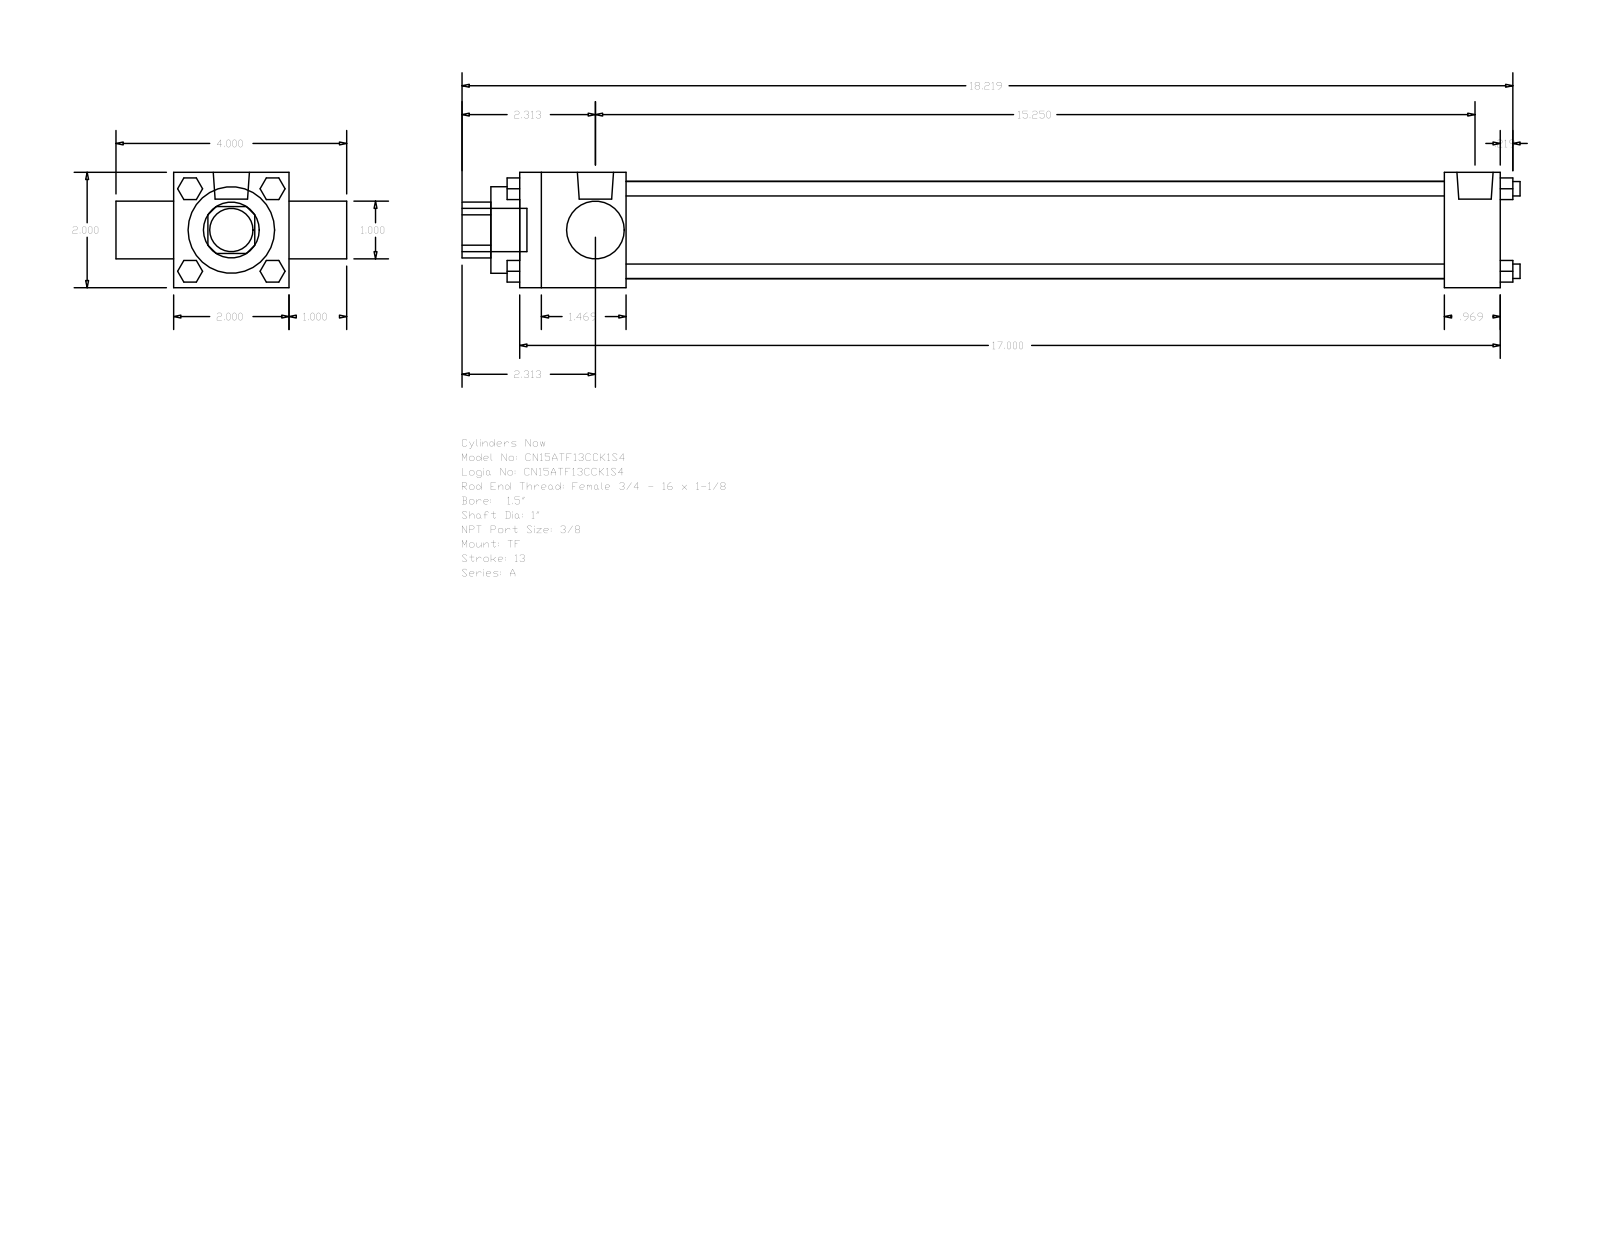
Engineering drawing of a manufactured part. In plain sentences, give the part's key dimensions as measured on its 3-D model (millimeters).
The part is named "A_TF__0150_1". Its 3-D file was written by "GSSL Pune (CONFIG_CONTROL_DESIGN)". It is 0 solids with 120 faces: 92 planar, 28 cylindrical and 0 other. Overall it measures 465.93 by 101.6 by 50.8 millimeters. Round holes: 2 of diameter 25.4, 1 of diameter 38.1, 1 of diameter 42.93. Round bosses or shafts: 4 of diameter 6.35, 3 of diameter 5.56, 2 of diameter 15.93, 1 of diameter 19.05. Partial cylindrical surfaces (rounded edges, fillets, slot ends): 1 of radius 12.29. The main face-to-face distances are 50.8, 25.4, 431.8, 76.2, 46.83, 407.19, 360.36, 384.97, 24.61, 12.7.
